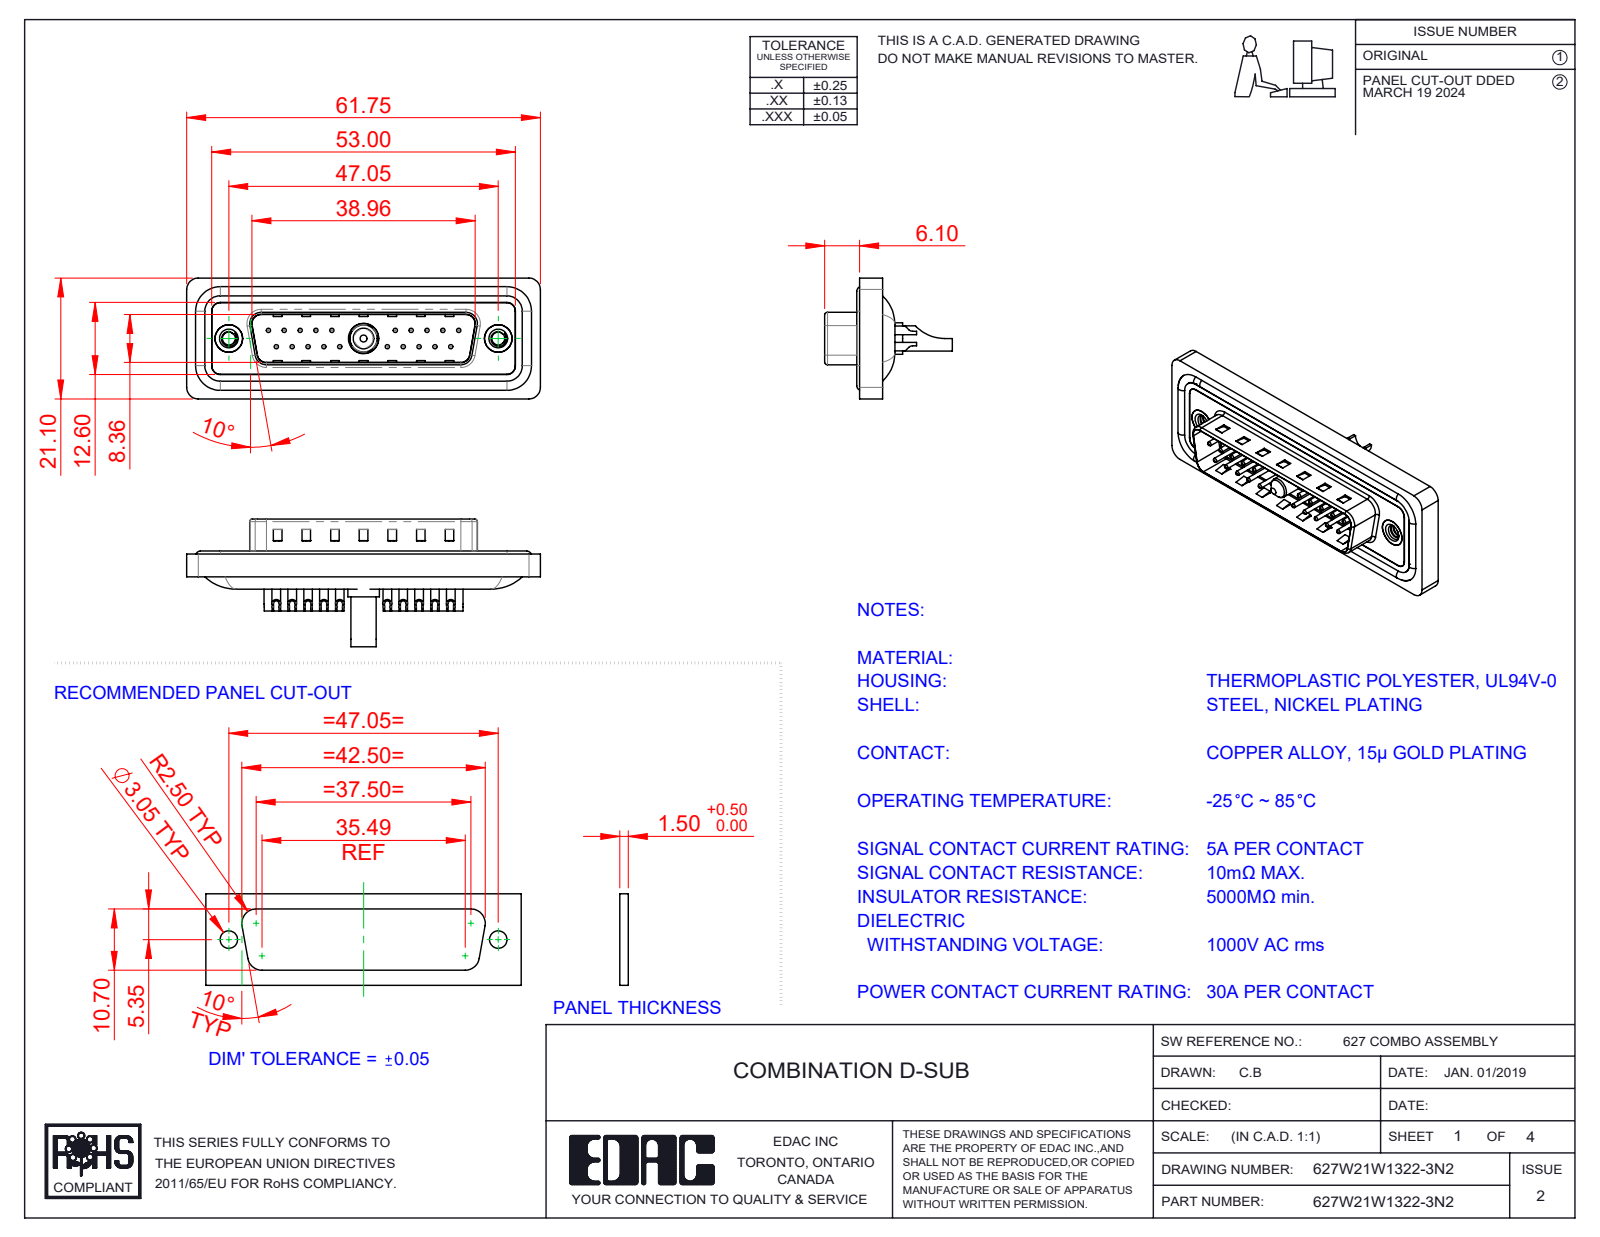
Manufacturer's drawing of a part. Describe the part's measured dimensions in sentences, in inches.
The part is named "627Combo Waterproof Housing_25 Contacts; Power Pin_30A SC; 627W21W1322-3N2; 627Combo Threaded Rivet_2 (+5 more)". Its 3-D file was written by "SolidWorks 2023 (CONFIG_CONTROL_DESIGN)". It is 29 solids with 1268 faces: 402 planar, 530 cylindrical and 336 other. Overall it measures 2.431 by 0.878 by 0.831 inches. Its volume is 0.443 cubic inches and its surface area 18.94 square inches. Round holes: 20 of diameter 0.03, 20 of diameter 0.039, 20 of diameter 0.063, 20 of diameter 0.079, 2 of diameter 0.089, 2 of diameter 0.157, 2 of diameter 0.189, 2 of diameter 0.197, 1 of diameter 0.138, 1 of diameter 0.191, 1 of diameter 0.209. Round bosses or shafts: 20 of diameter 0.059, 4 of diameter 0.063, 2 of diameter 0.193, 1 of diameter 0.217, 1 of diameter 0.205, 1 of diameter 0.187, 1 of diameter 0.173, 1 of diameter 0.148. Partial cylindrical surfaces (rounded edges, fillets, slot ends): 22 of radius 0.059, 18 of radius 0.079, 8 of radius 0.02, 8 of radius 0.063, 6 of radius 0.039, 4 of radius 0.01, 4 of radius 0.024, 4 of radius 0.026. The main face-to-face distances are 0.016, 0.059, 0.043, 0.063, 0.02, 0.122, 0.114, 0.161, 0.032, 0.377. The hole center spacings are 0.124, 0.109, 0.218, 0.327, 0.198, 0.763, 0.826, 0.872.
